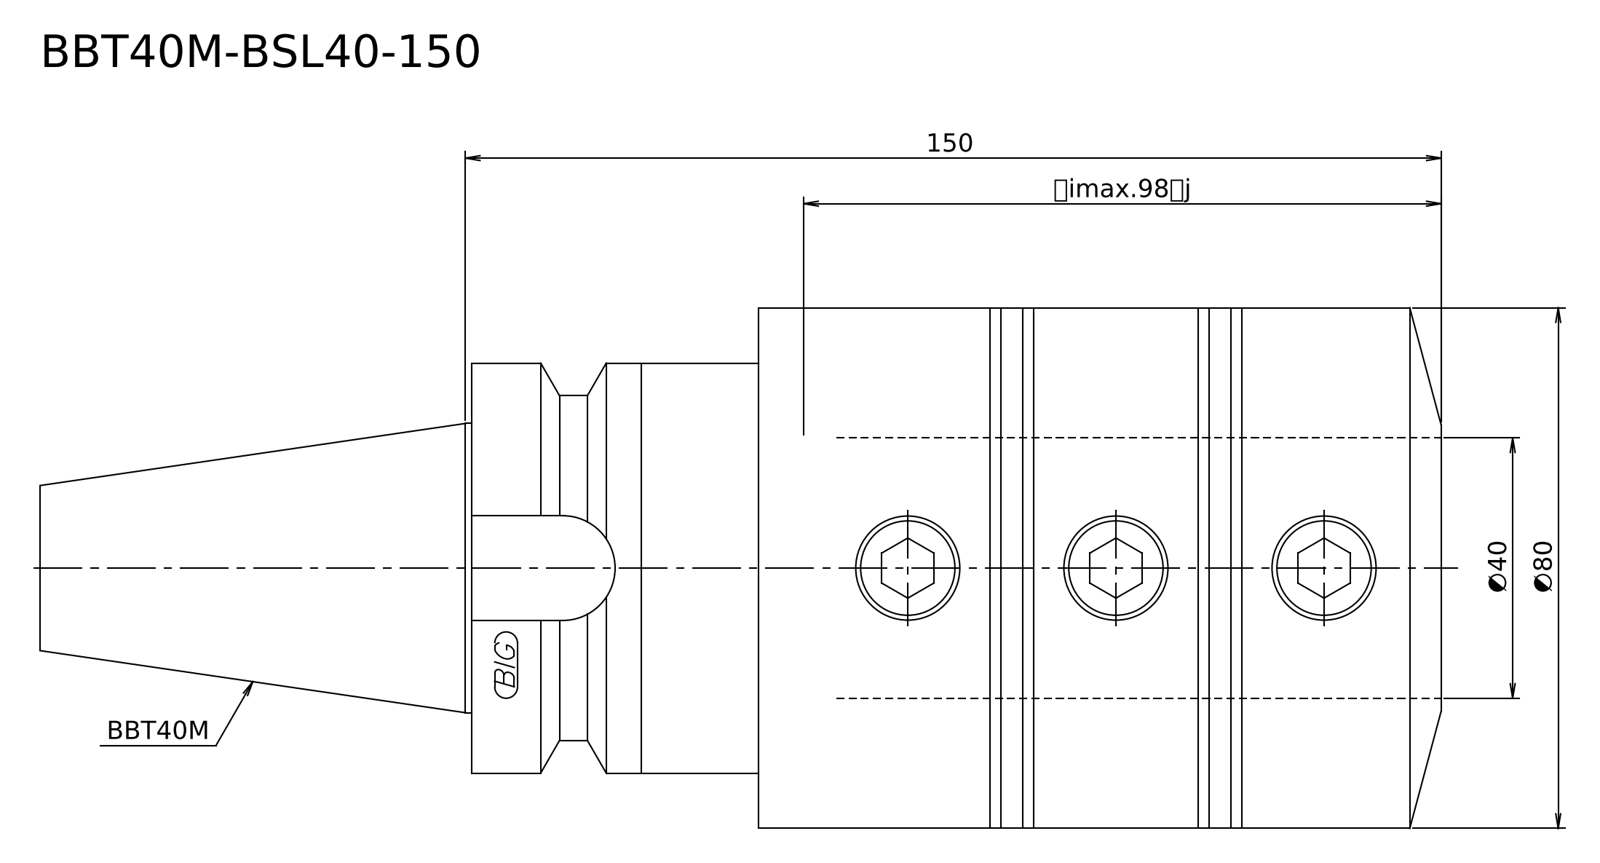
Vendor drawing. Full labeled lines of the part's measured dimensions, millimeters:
STEP written by: Kubotek KeyCreator V8.5.1 (14335) (CONFIG_CONTROL_DESIGN)
Units: millimetres
Bodies: 1 solid, 13 faces (4 planar, 5 cylindrical, 4 other)
Overall size (bounding box): 215.4 × 80 × 80
Volume: 714 834 mm³ · Surface area: 51 234 mm²
Round bosses / shafts (diameter × count): ⌀80 ×1, ⌀63 ×1, ⌀53 ×1, ⌀44.45 ×1
Main face-to-face distances: 44, 105, 149, 215.4, 110.4, 66.4
